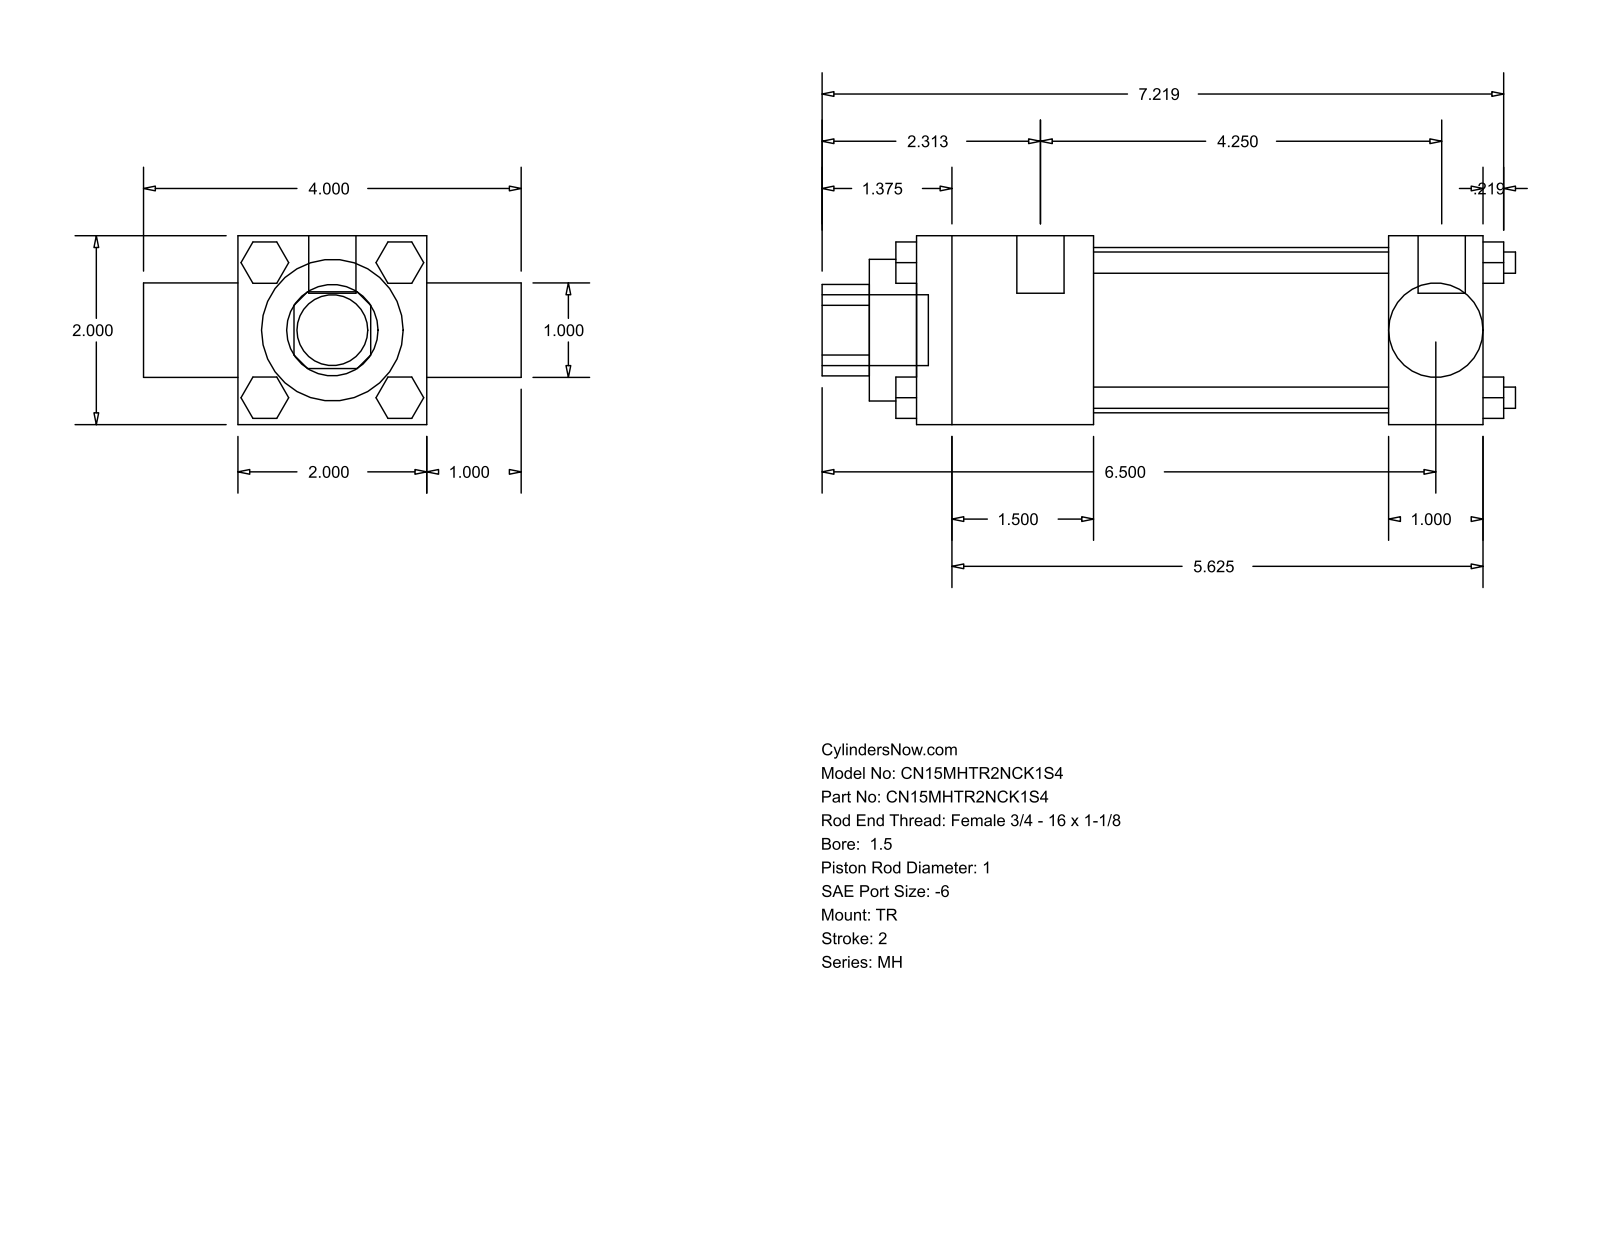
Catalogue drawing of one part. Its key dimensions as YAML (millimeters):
part_name: "MH_TR__0150_1"
step_written_by: "GSSL Pune (CONFIG_CONTROL_DESIGN)"
units: millimeters
bodies: {solids: 0, faces: 120, planar: 92, cylindrical: 28, other: 0}
overall_size: [186.53, 101.6, 50.8]
round_holes:
  - {diameter: 25.35, count: 1}
  - {diameter: 25.4, count: 1}
  - {diameter: 38.1, count: 1}
  - {diameter: 44.45, count: 1}
round_bosses_or_shafts:
  - {diameter: 5.71, count: 4}
  - {diameter: 5.56, count: 3}
  - {diameter: 12.7, count: 2}
  - {diameter: 19.05, count: 1}
partial_cylinders:
  - {radius: 12.29, count: 1}
face_to_face_distances: [50.8, 25.4, 152.4, 76.2, 47.63, 104.77, 127, 79.37, 157.96, 12.7]
